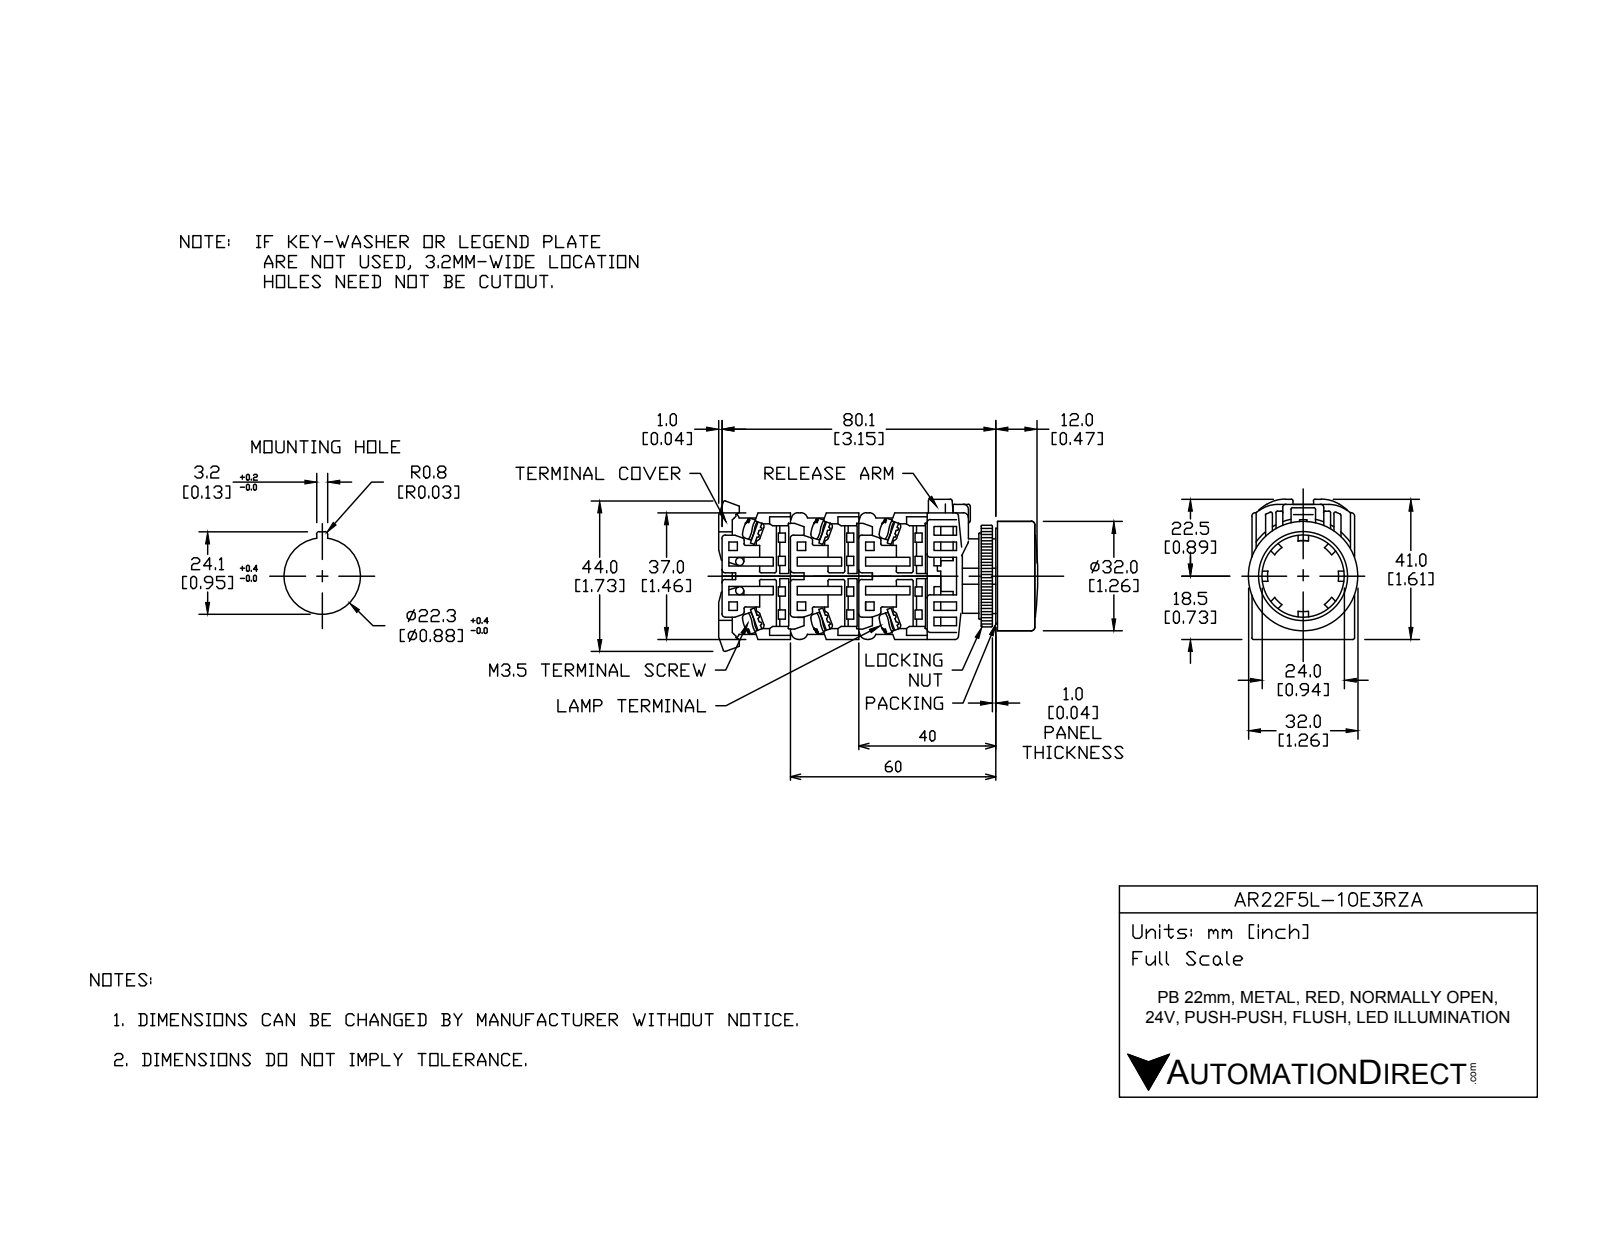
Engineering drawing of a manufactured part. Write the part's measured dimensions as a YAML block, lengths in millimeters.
part_name: "AR22F5L-10E3RZA"
step_written_by: "SolidWorks 2017 (AUTOMOTIVE_DESIGN)"
units: millimeters
bodies: {solids: 18, faces: 475, planar: 329, cylindrical: 111, other: 35}
overall_size: [52.75, 43.81, 32]
volume: 36367
surface_area: 24064
round_holes:
  - {diameter: 21.8, count: 1}
  - {diameter: 22, count: 1}
  - {diameter: 25, count: 1}
  - {diameter: 31, count: 1}
round_bosses_or_shafts:
  - {diameter: 5, count: 4}
  - {diameter: 32, count: 1}
  - {diameter: 30.5, count: 1}
  - {diameter: 29.8, count: 1}
  - {diameter: 24, count: 1}
  - {diameter: 23.8, count: 1}
  - {diameter: 21.75, count: 1}
  - {diameter: 17, count: 1}
partial_cylinders:
  - {radius: 0.5, count: 39}
  - {radius: 1.75, count: 8}
  - {radius: 5, count: 4}
  - {radius: 4, count: 2}
  - {radius: 16.59, count: 1}
  - {radius: 17.59, count: 1}
face_to_face_distances: [1, 18, 28.5, 48.5, 20, 29, 3, 2, 21, 0.5]
